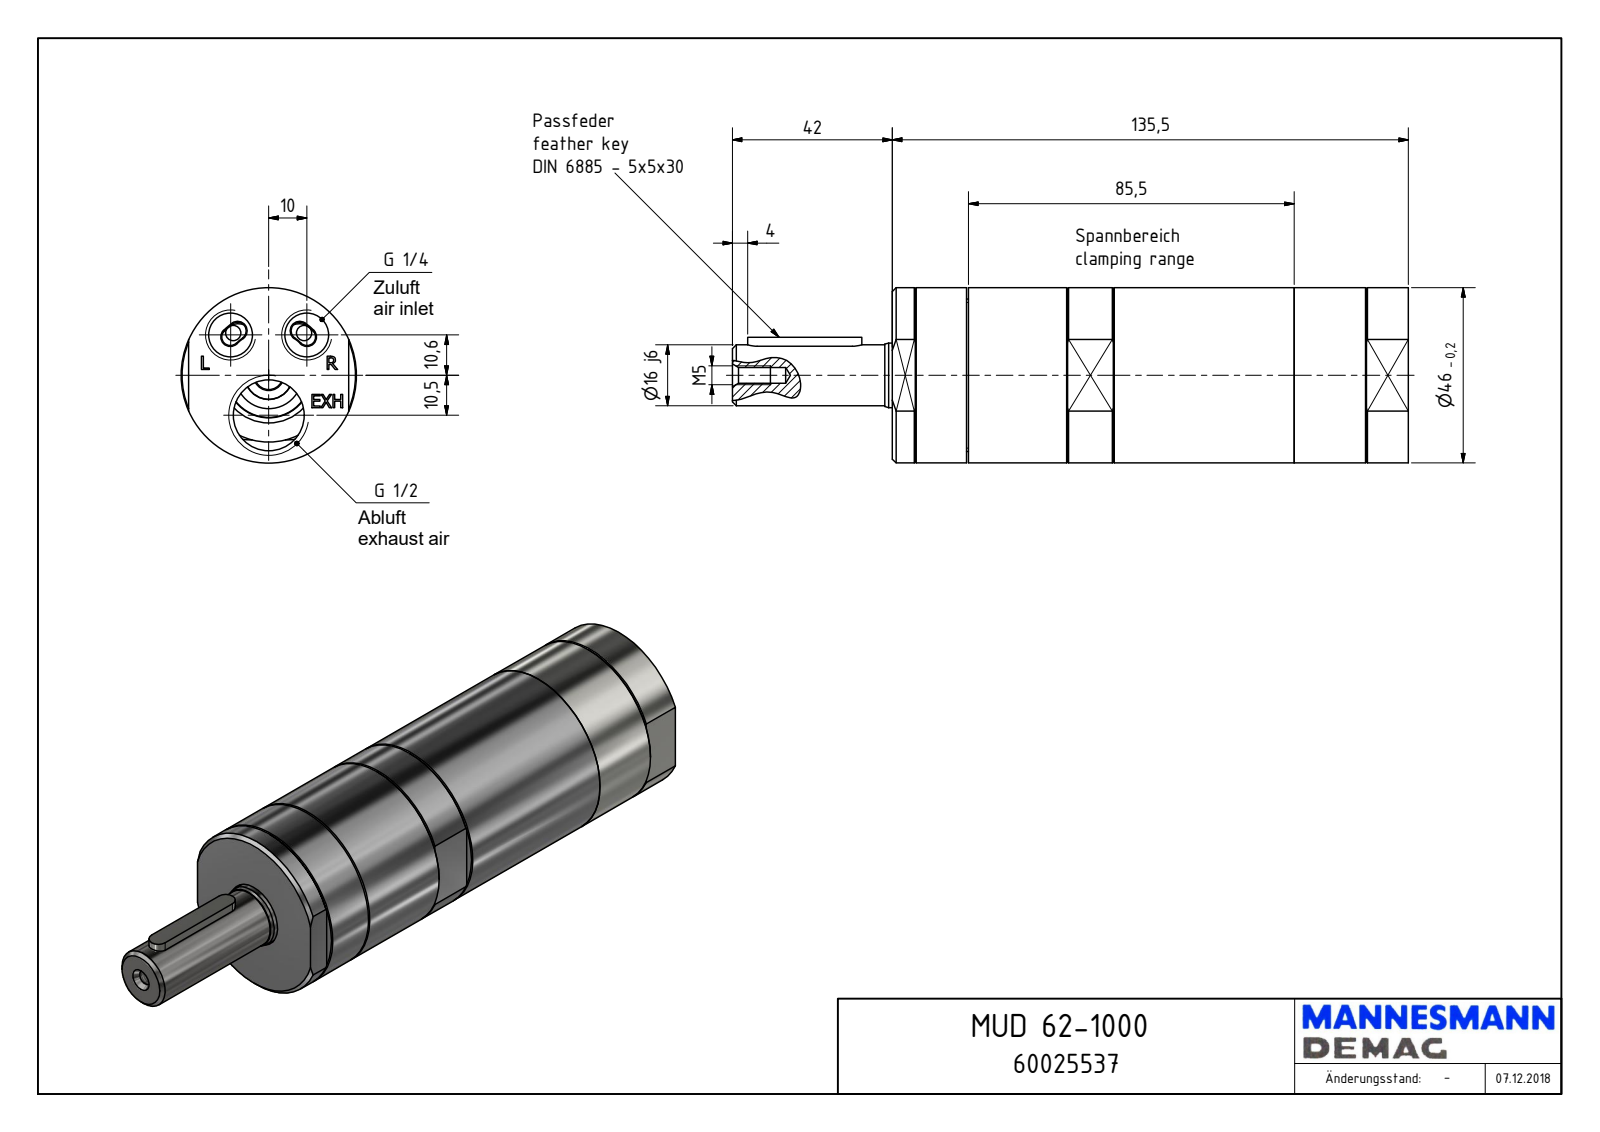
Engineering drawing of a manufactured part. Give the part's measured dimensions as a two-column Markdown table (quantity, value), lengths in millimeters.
| quantity | value |
| --- | --- |
| part name | Bauteil1 |
| STEP written by | Autodesk Inventor 2018 (AUTOMOTIVE_DESIGN) |
| units | millimeters |
| bodies | 1 solid, 163 faces (96 planar, 31 cylindrical, 36 other) |
| overall size | 177.5 × 46 × 46 |
| volume | 227 182 mm³ |
| surface area | 29 532 mm² |
| round holes (diameter × count) | 11.45 × 2, 4.13 × 1, 17.5 × 1, 18.63 × 1, 21.5 × 1, 23 × 1 |
| round bosses / shafts (diameter × count) | 46 × 1, 40 × 1, 33.42 × 1, 19.56 × 1, 16.95 × 1, 16 × 1 |
| partial cylindrical surfaces (radius × count) | 2.5 × 2, 5 × 2, 19 × 1 |
| main face-to-face distances | 135.5, 42, 20, 115.5, 19.5, 0.5, 116, 128.21, 108.71, 108.21 |
| hole center spacings | 14.57, 23.35, 10.5, 20 |
